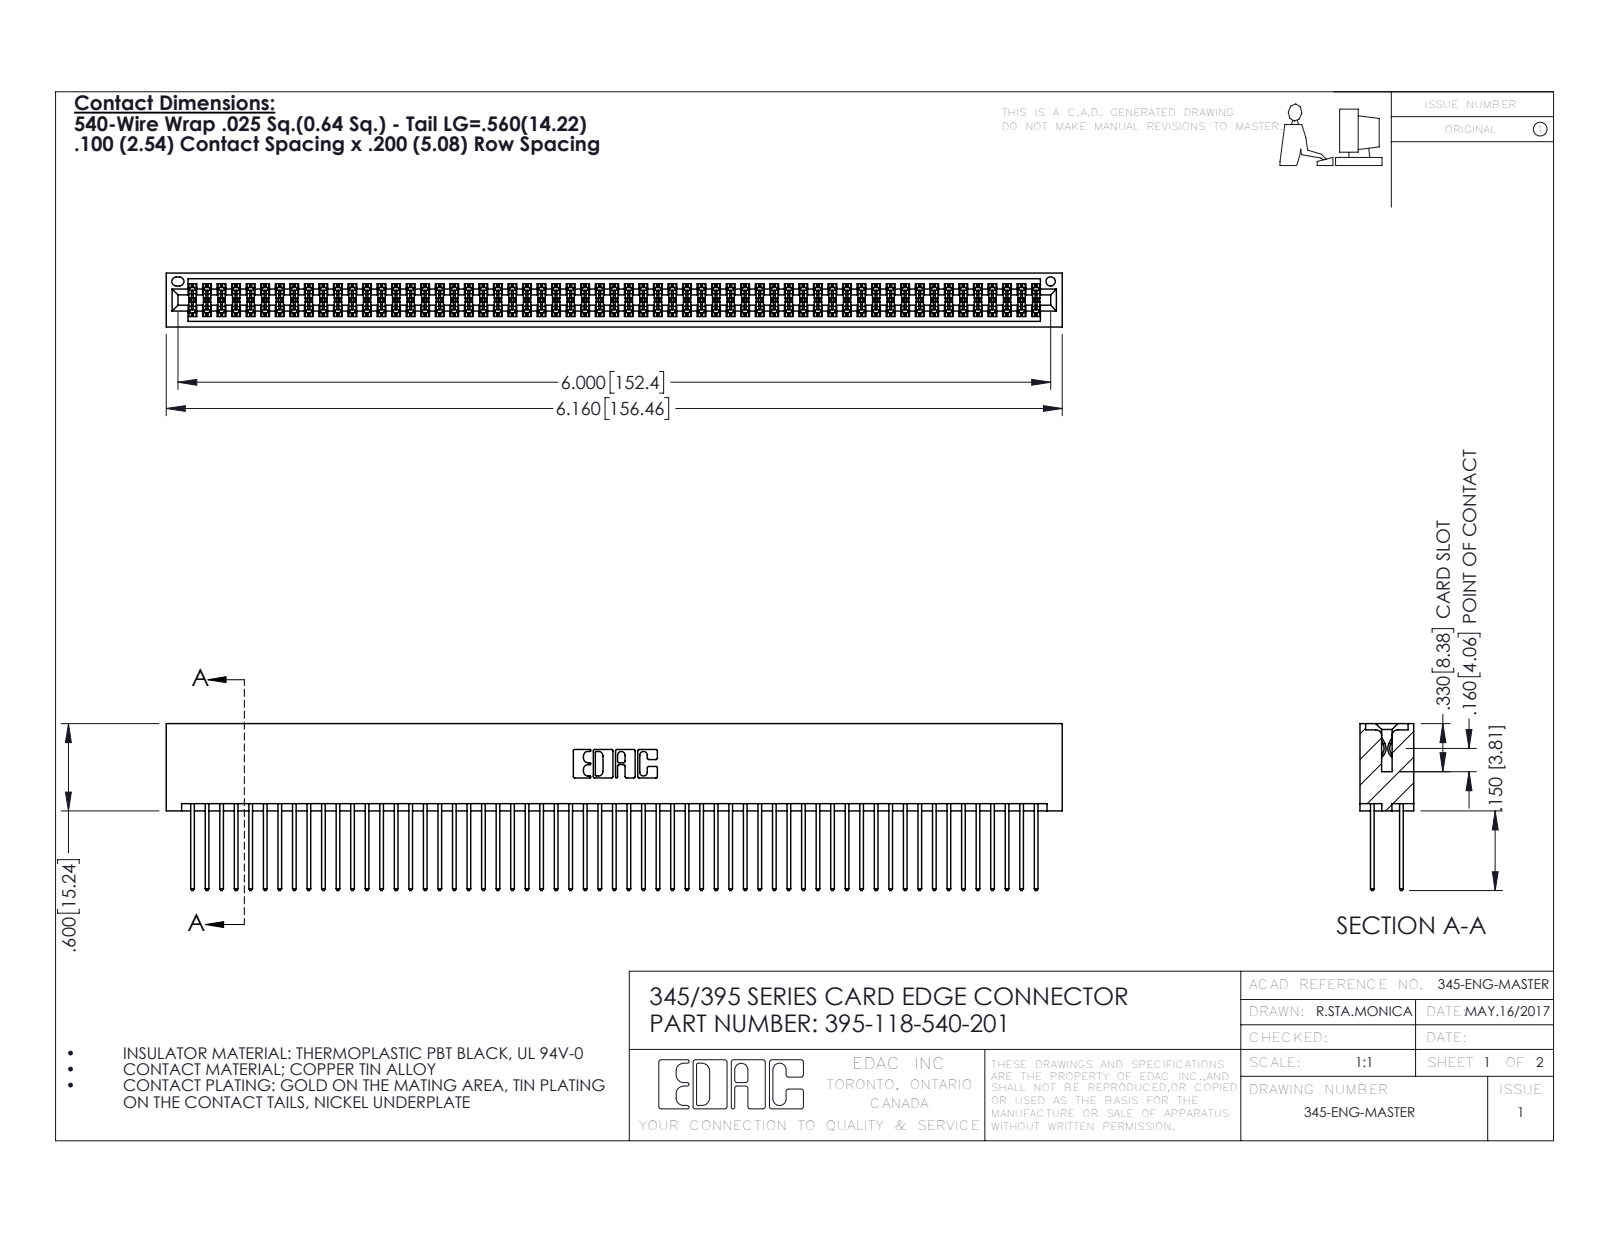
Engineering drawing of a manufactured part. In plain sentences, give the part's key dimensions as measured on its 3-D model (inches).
The part is named "345-292-001_345-293-140; 395-118-540-201; 345 Part_No Mounting Lugs". Its 3-D file was written by "SolidWorks 2016 (CONFIG_CONTROL_DESIGN)". It is 119 solids with 6018 faces: 3970 planar, 2048 cylindrical and 0 other. Overall it measures 6.16 by 1.147 by 0.37 inches. Its volume is 1.002 cubic inches and its surface area 41.82 square inches. Round holes: 1 of diameter 0.064. Partial cylindrical surfaces (rounded edges, fillets, slot ends): 177 of radius 0.006, 118 of radius 0.01, 22 of radius 0.01, 6 of radius 0.007, 6 of radius 0.031, 3 of radius 0.026, 2 of radius 0.014, 2 of radius 0.019. The main face-to-face distances are 0.298, 0.072, 0.2, 0.098, 0.272, 0.025, 0.225, 0.37, 0.175, 0.149.
